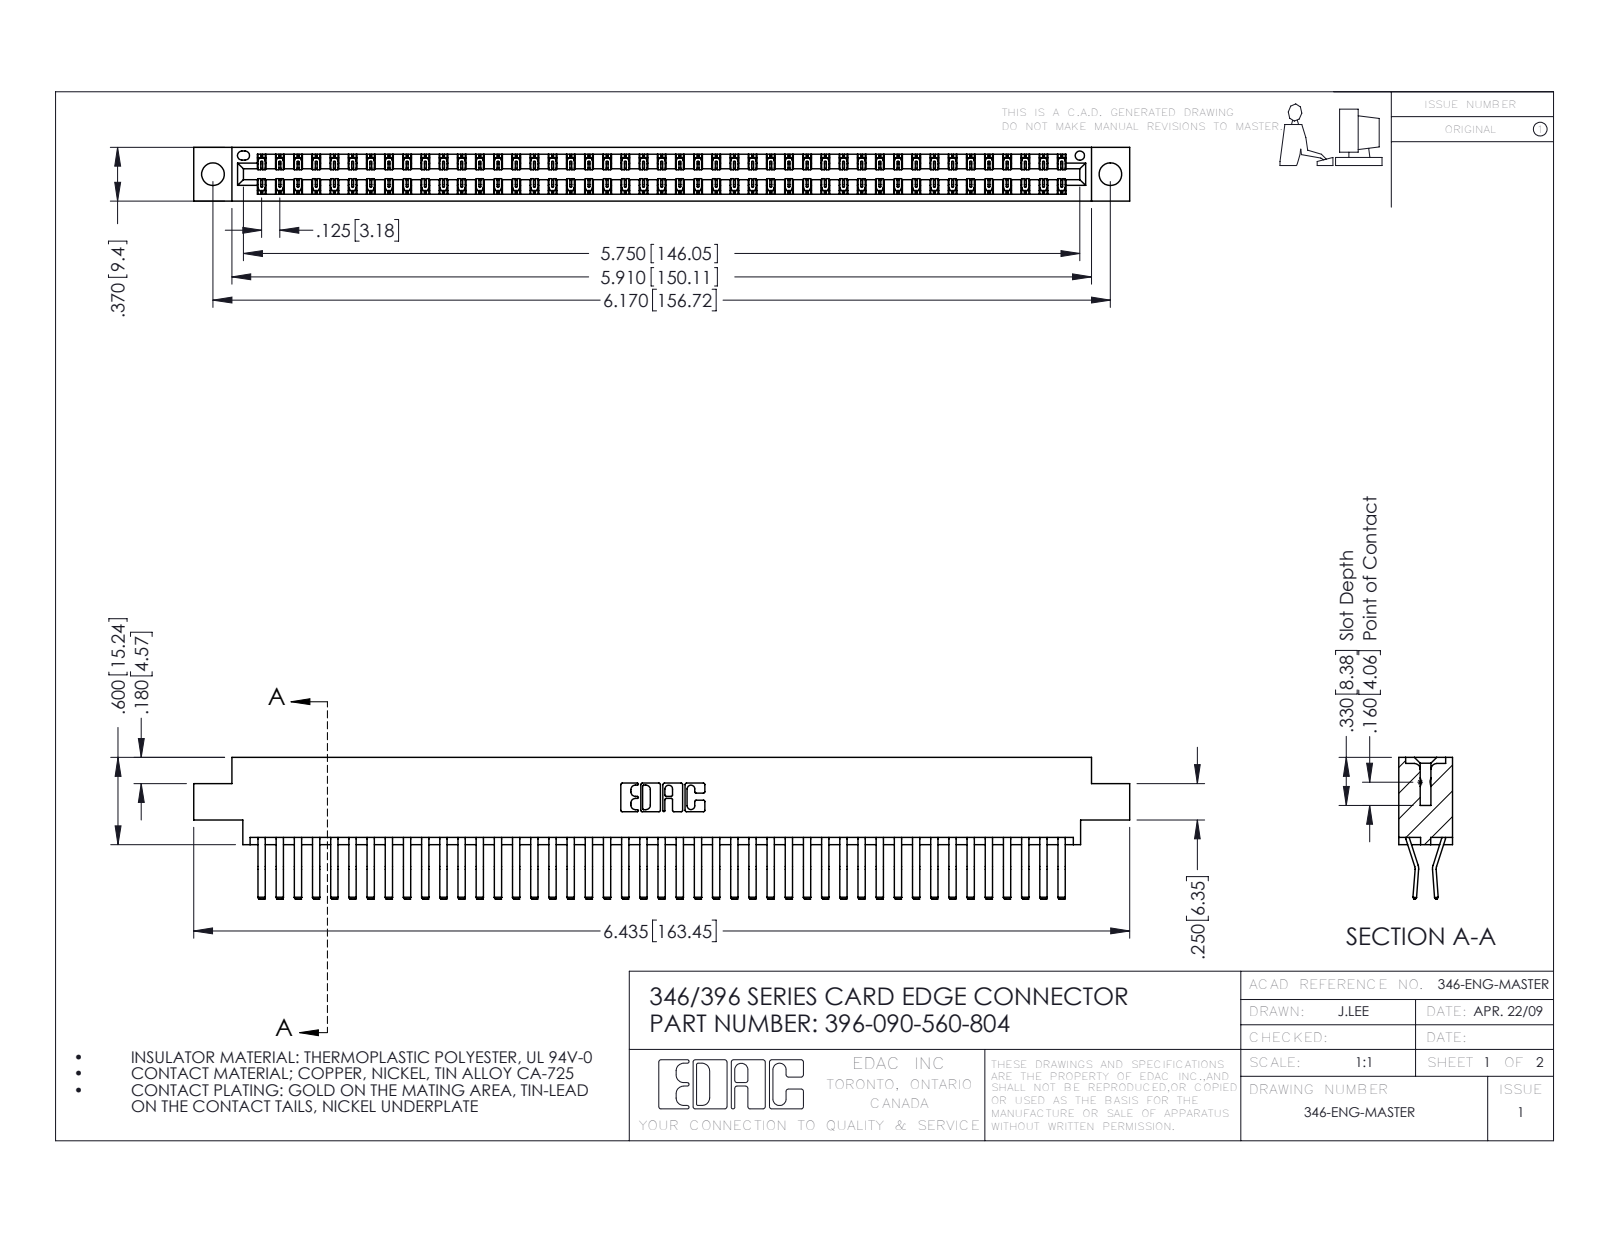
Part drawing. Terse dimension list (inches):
name: 346 Part_0.170 Offset - 0.156 Dia-TH; 345-292-001_560 Tail; 396-090-560-804
written by: SolidWorks 2016 (CONFIG_CONTROL_DESIGN)
unit: in
bodies: 91 solids, 4986 faces (3230 planar, 1756 cylindrical, 0 other)
size: 6.435 × 0.975 × 0.37
volume: 0.995 in³; area: 37.25 in²
holes: 2× ⌀0.156, 1× ⌀0.064
rounds: 135× R0.006, 22× R0.01, 6× R0.007, 6× R0.031, 3× R0.026, 2× R0.01, 2× R0.014, 2× R0.022
face distances: 0.048, 0.322, 0.37, 0.025, 0.25, 0.072, 0.298, 0.275, 0.148, 0.222
hole spacings: 0.246, 5.961, 6.17
